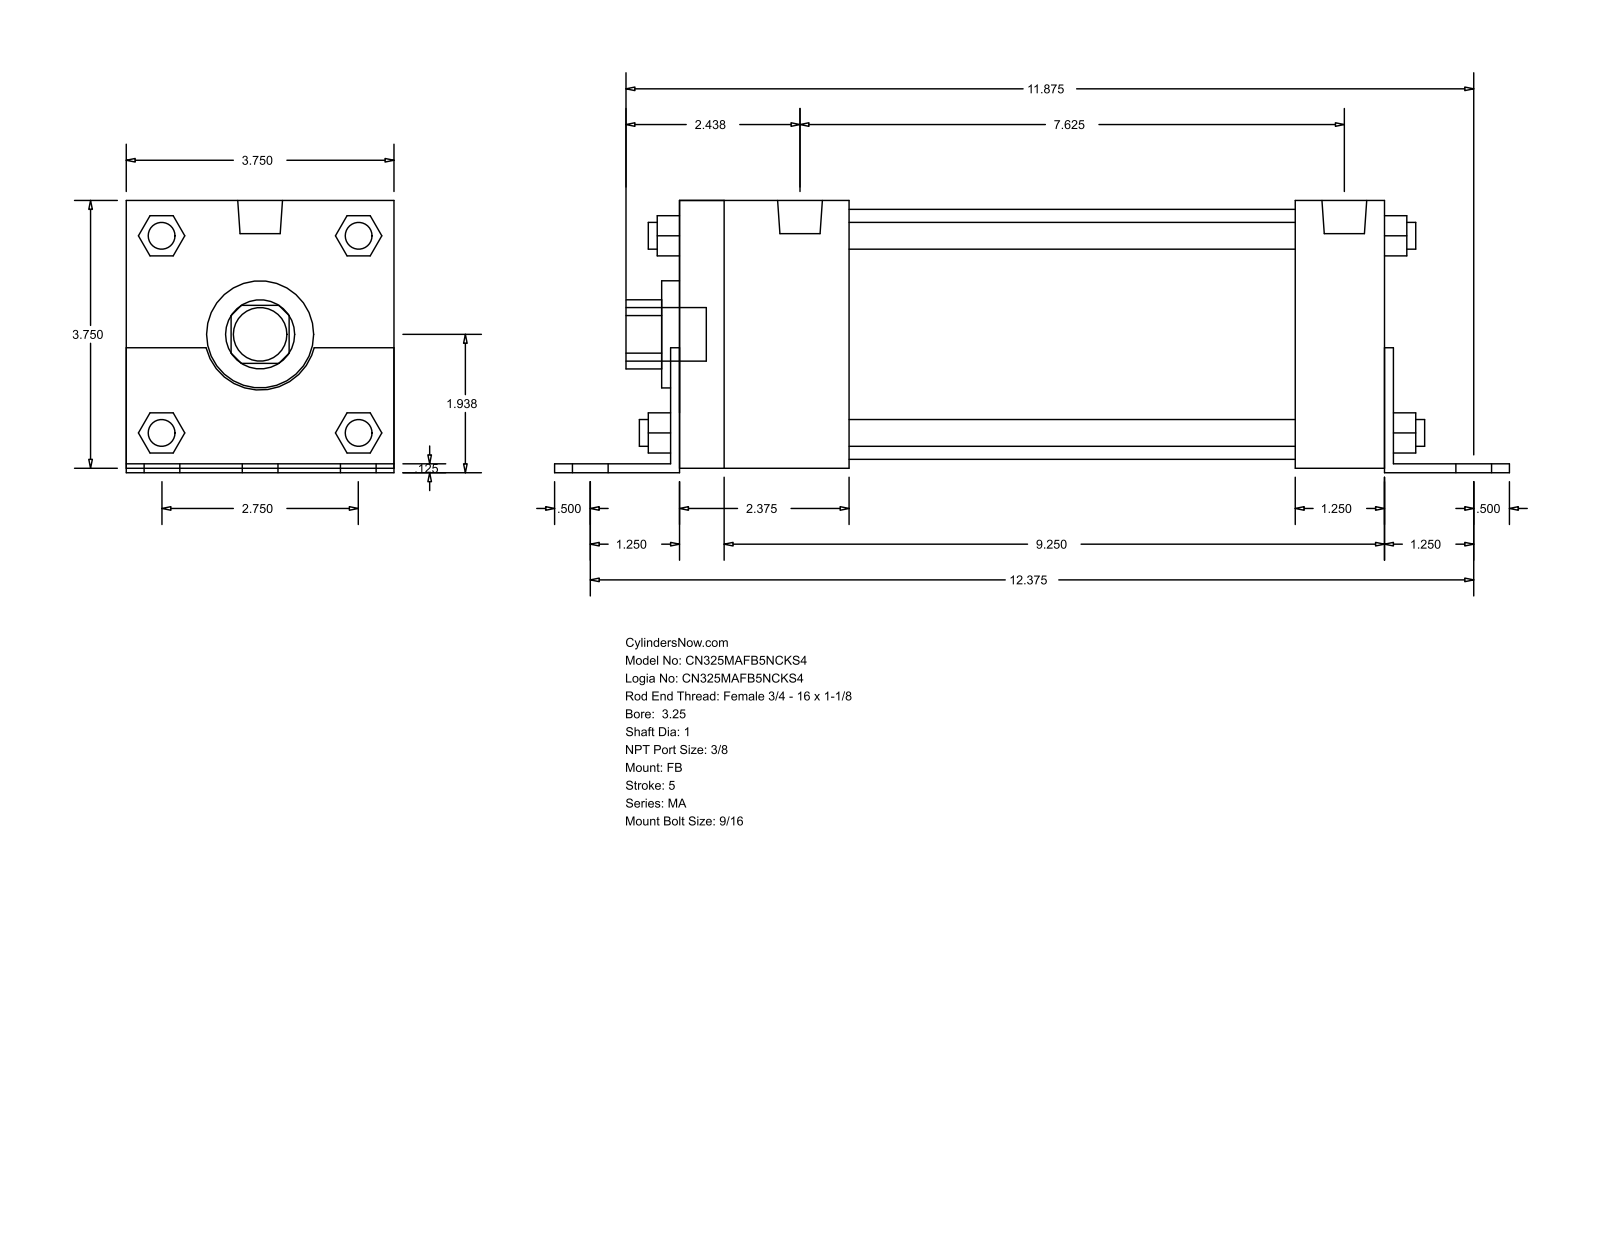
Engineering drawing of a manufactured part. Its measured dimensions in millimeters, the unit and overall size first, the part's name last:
Units: millimetres
Overall size (bounding box): 339.73 × 96.84 × 95.25
Round holes (diameter × count): ⌀25.4 ×1, ⌀38.1 ×1, ⌀88.9 ×1
Round bosses / shafts (diameter × count): ⌀14.29 ×6, ⌀11.11 ×4, ⌀9.53 ×4, ⌀15.93 ×2, ⌀19.05 ×1
Partial cylindrical surfaces — rounded edges, fillets, slot ends (radius × count): R12.29 ×1, R19.81 ×1
Main face-to-face distances: 95.24, 3.17, 1.59, 96.83, 1.58, 93.66, 254, 250.83, 257.17, 34.93
Bodies: 0 solids, 140 faces (105 planar, 35 cylindrical, 0 other)
Part name (STEP PRODUCT): MA_FB__0325_1
STEP written by: GSSL Pune (CONFIG_CONTROL_DESIGN)
